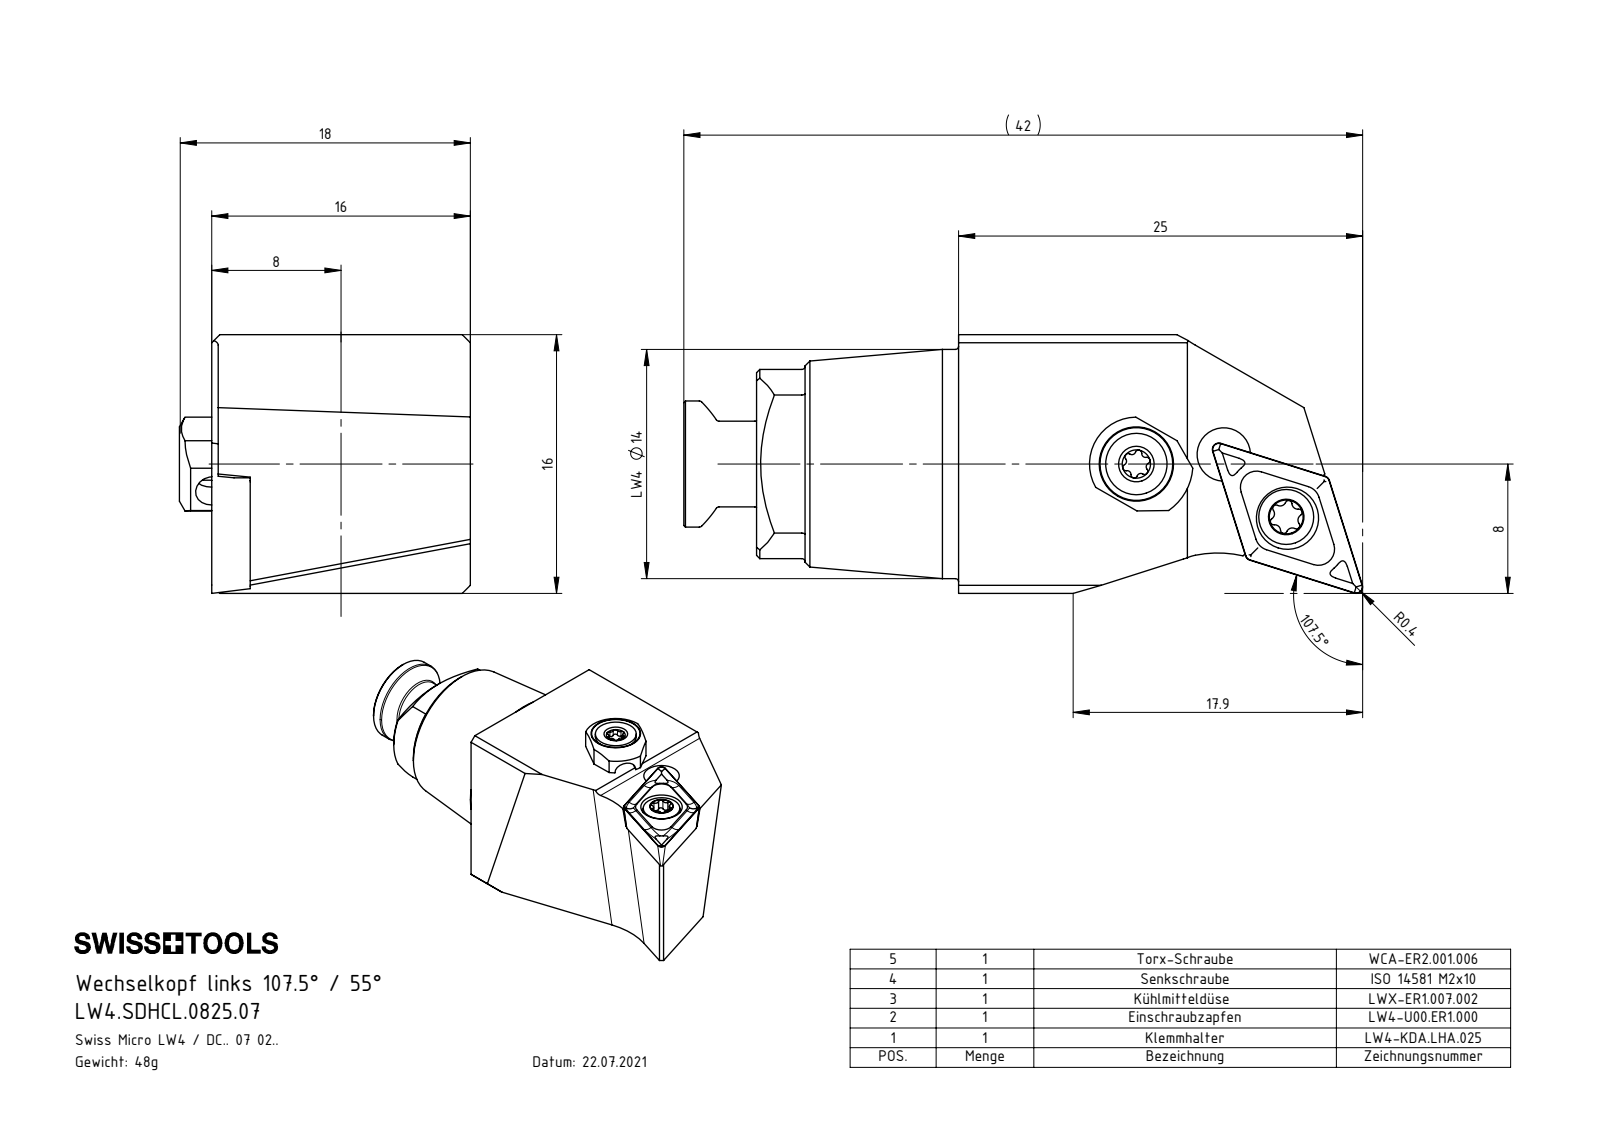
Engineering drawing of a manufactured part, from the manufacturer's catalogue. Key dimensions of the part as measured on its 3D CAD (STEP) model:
Part name (STEP PRODUCT): LW4.SDHCL.0825.07; ISO 14581 - M2x10; DCMT070204; WCA-ER2.001.006_A (+3 more)
STEP written by: SolidWorks 2022 (CONFIG_CONTROL_DESIGN)
Units: millimetres
Bodies: 6 solids, 258 faces (70 planar, 80 cylindrical, 108 other)
Overall size (bounding box): 42 × 18 × 16
Volume: 6 170 mm³ · Surface area: 3 456 mm²
Round holes (diameter × count): ⌀3 ×2, ⌀1.6 ×1, ⌀2 ×1, ⌀2.05 ×1, ⌀2.5 ×1, ⌀2.8 ×1, ⌀3.3 ×1, ⌀3.85 ×1, ⌀5.5 ×1
Round bosses / shafts (diameter × count): ⌀14.17 ×1, ⌀7.7 ×1, ⌀6 ×1, ⌀5.3 ×1, ⌀5 ×1, ⌀3.8 ×1, ⌀3.4 ×1, ⌀2.5 ×1
Partial cylindrical surfaces — rounded edges, fillets, slot ends (radius × count): R0.2 ×8, R0.21 ×6, R0.24 ×6, R0.36 ×4, R0.36 ×2, R0.5 ×1, R1 ×1, R2.9 ×1
Main face-to-face distances: 16, 13.62, 2.38, 7.5, 15.6, 1.98, 0.4, 2, 12.5, 4
Hole centre spacings: 5.44, 5.46, 5.57, 9.83, 9.93
